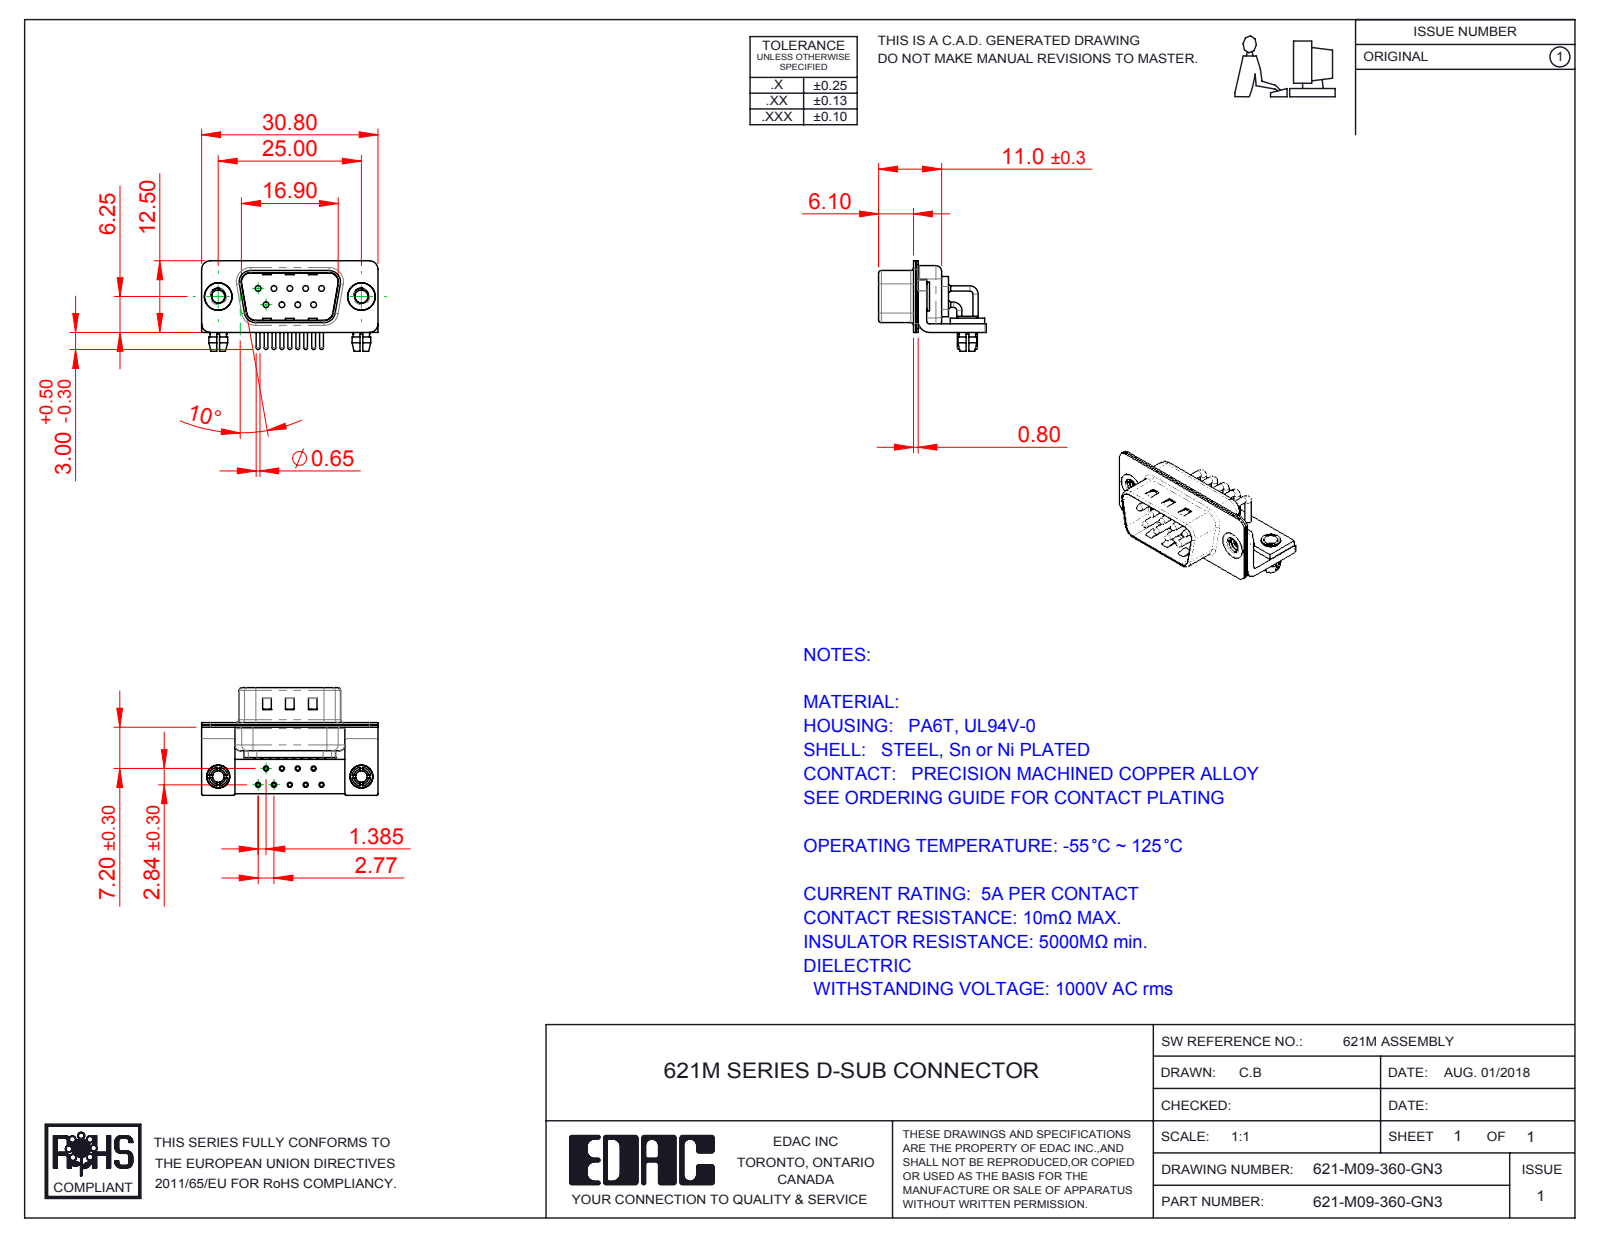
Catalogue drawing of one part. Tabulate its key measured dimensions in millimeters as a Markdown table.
| quantity | value |
| --- | --- |
| part name | 621-M09-360-GN3; 621M Board Lock; 621M Stabilizer Board_09 Contacts; 621M Stabilizer Bracket (+6 more) |
| STEP written by | SolidWorks 2016 (CONFIG_CONTROL_DESIGN) |
| units | millimeters |
| bodies | 19 solids, 1454 faces (757 planar, 525 cylindrical, 172 other) |
| overall size | 30.8 × 18.8 × 15.8 |
| volume | 1 801 mm³ |
| surface area | 5 055 mm² |
| round holes (diameter × count) | 2 × 11, 0.9 × 9, 1 × 9, 1.7 × 9, 2.26 × 2, 2.5 × 2, 3.2 × 2, 4 × 2, 4.8 × 2 |
| round bosses / shafts (diameter × count) | 1.5 × 9, 0.9 × 9, 0.65 × 9, 5 × 2, 4.9 × 2, 4 × 2, 3.4 × 2, 3.3 × 2 |
| partial cylindrical surfaces (radius × count) | 0.25 × 16, 1.5 × 16, 2 × 13, 0.5 × 9, 1.01 × 9, 1.6 × 8, 0.6 × 4, 0.65 × 4 |
| main face-to-face distances | 0.4, 1.5, 0.8, 0.85, 1.25, 1, 10.4, 9.55, 2.5, 1.9 |
| hole center spacings | 3.16, 2.77, 5.54, 5.03, 5.04, 8.31, 7.48, 7.49 |
